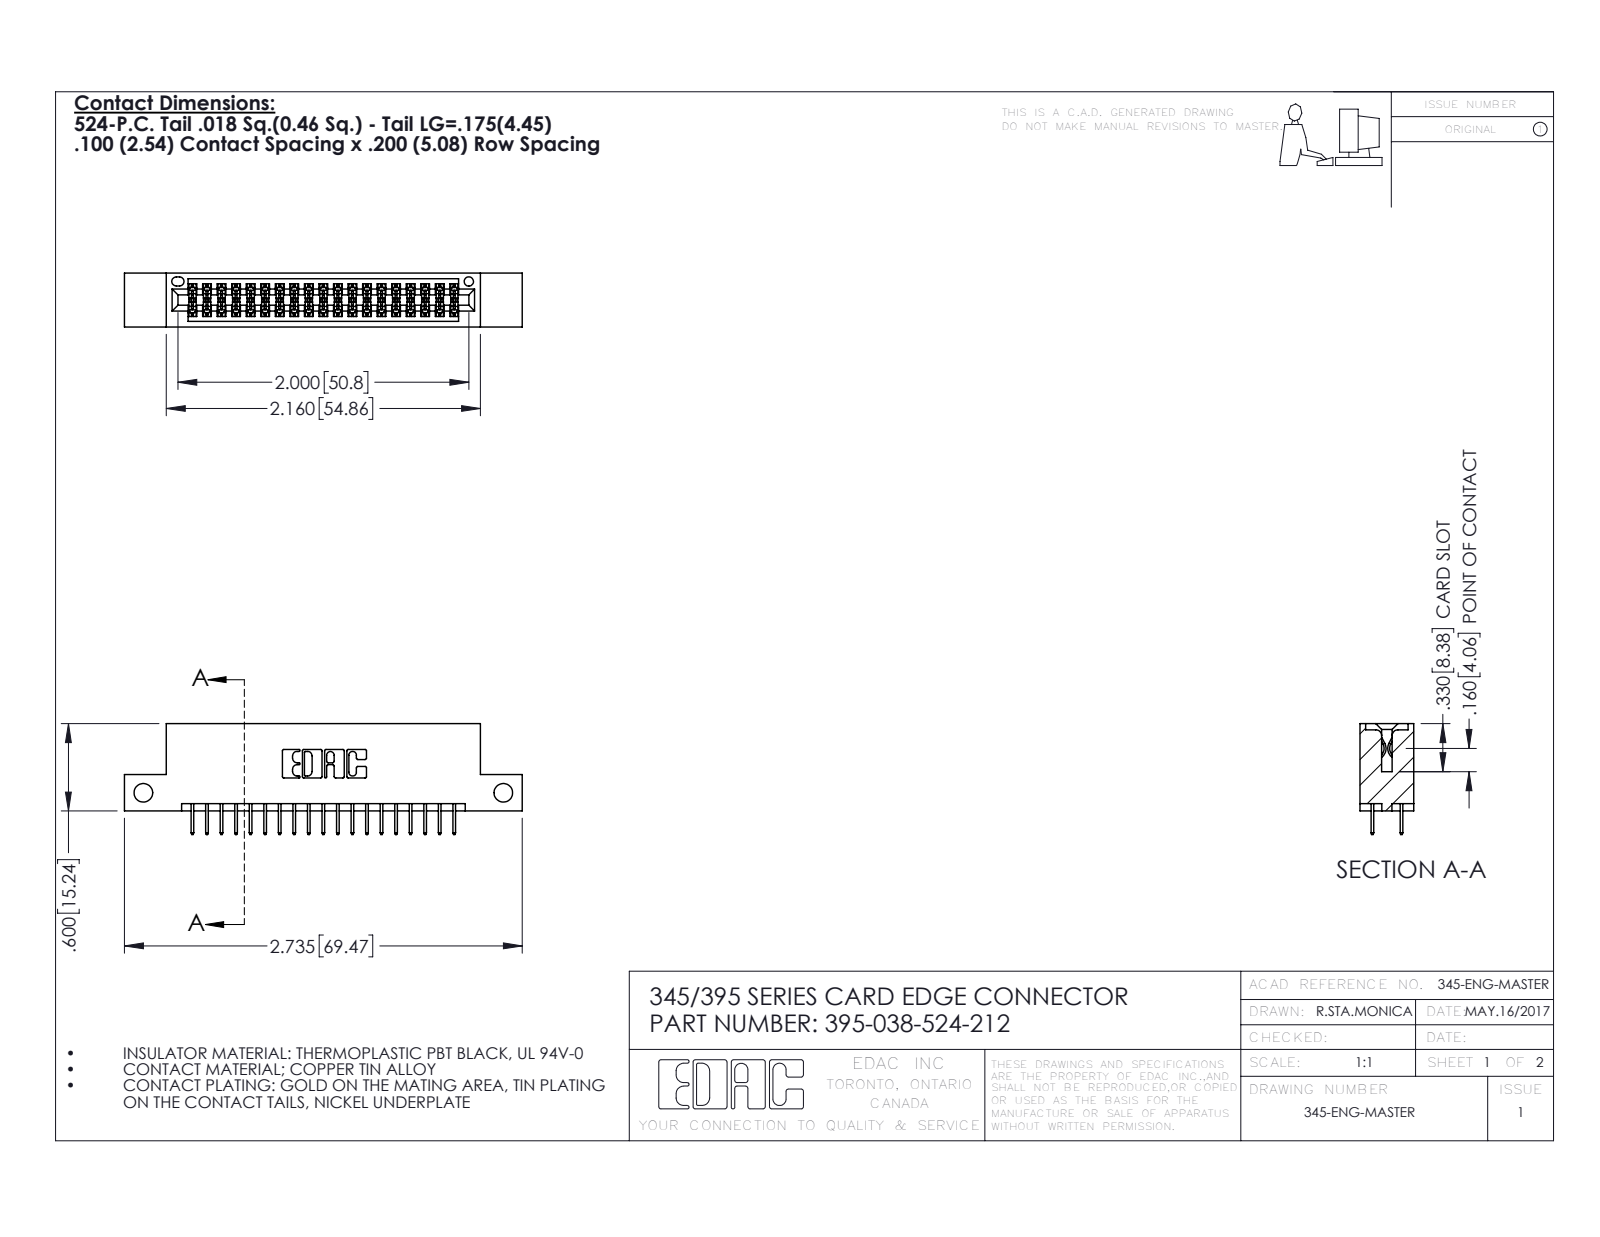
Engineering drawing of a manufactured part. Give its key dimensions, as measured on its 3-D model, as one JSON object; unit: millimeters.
{"part_name": "345 Part_Flush Mounting Lugs - Side Mount; 345-292-001_345-293-124; 395-038-524-212", "step_written_by": "SolidWorks 2016 (CONFIG_CONTROL_DESIGN)", "units": "millimeters", "bodies": {"solids": 39, "faces": 2178, "planar": 1562, "cylindrical": 616, "other": 0}, "overall_size": [69.5, 19.4, 9.4], "volume_mm3": 6390, "surface_area_mm2": 8710, "round_holes": [[3.3, 2], [1.6, 1]], "partial_cylinders_radius": [[0.2, 57], [0.3, 22], [0.2, 6], [0.8, 6], [0.7, 3], [0.4, 2], [0.5, 2], [0.6, 2]], "face_to_face_distances": [7.6, 1.8, 5.1, 9.4, 2.5, 6.9, 0.6, 5.7, 1.8, 4.4], "hole_center_spacings": [62.9]}
